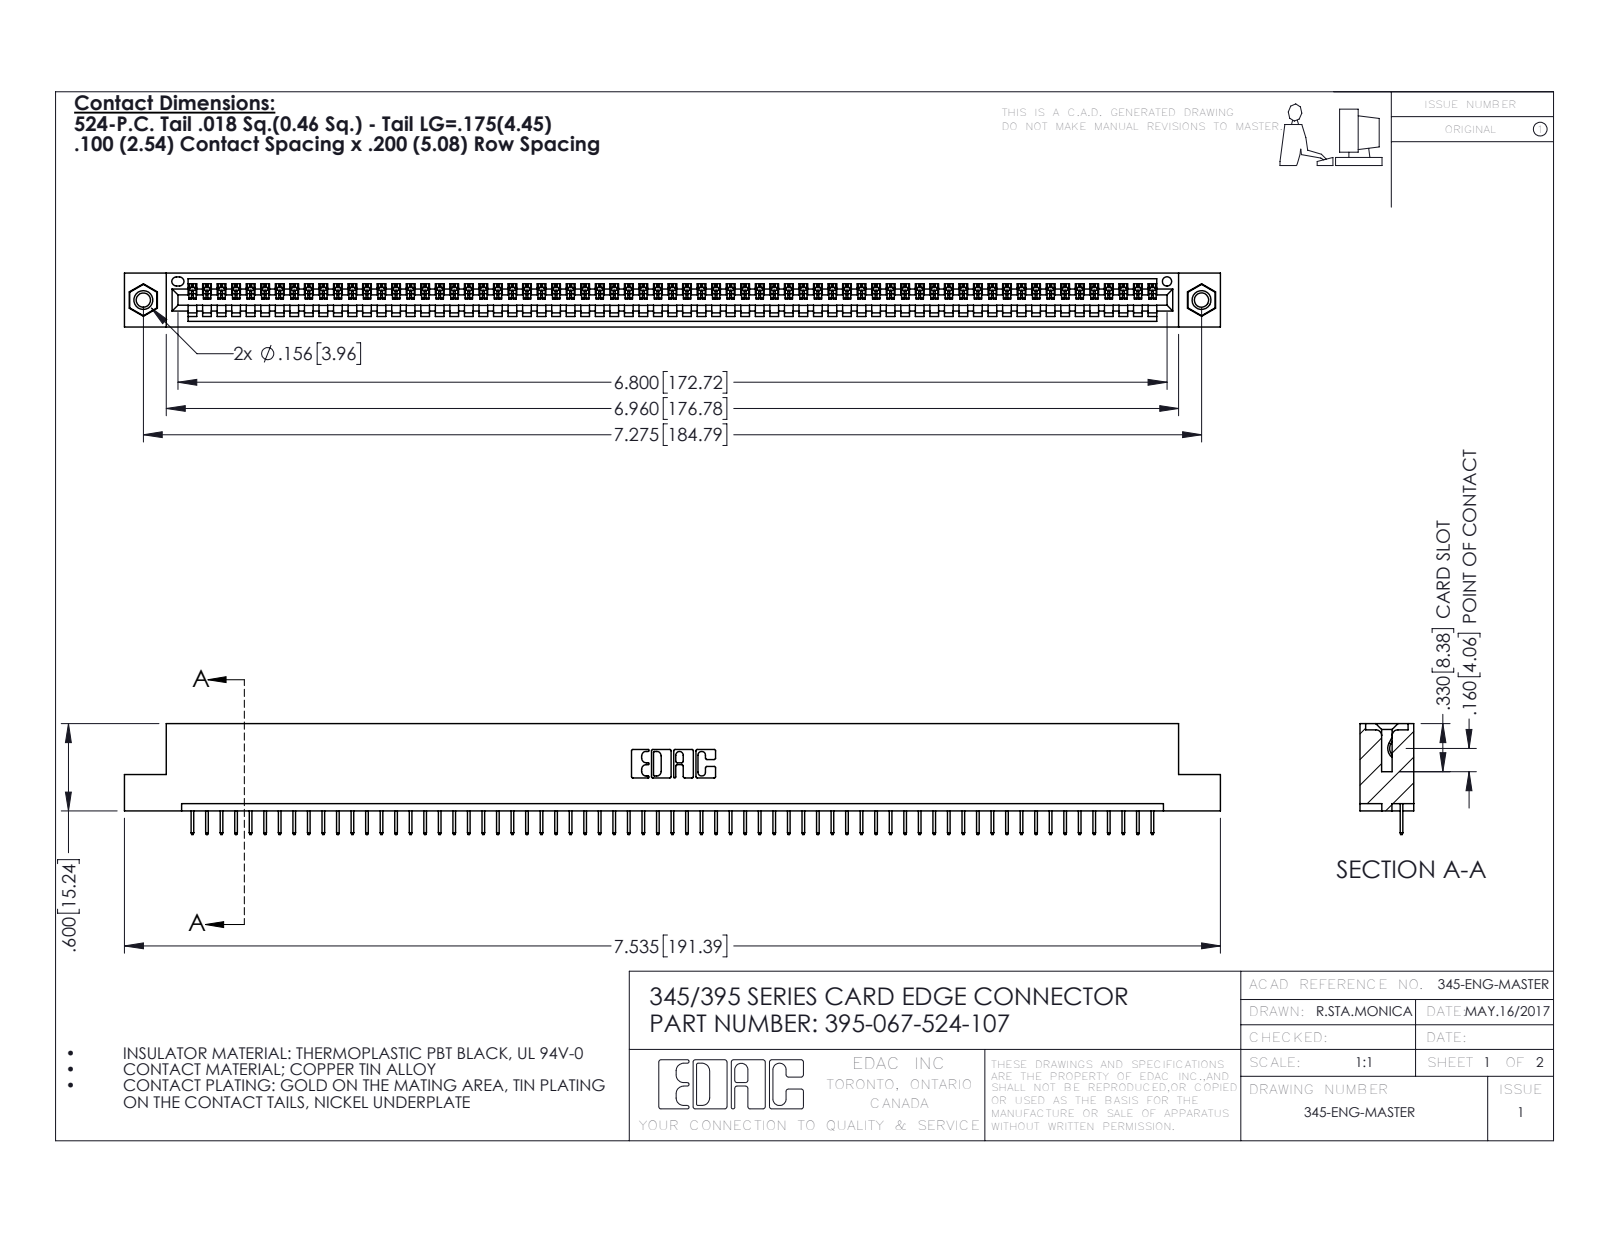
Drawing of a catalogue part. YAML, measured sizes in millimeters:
part_name: "345-292-001_345-293-124; 345 Part_Flush Mounting Lugs - 0.156 Dia-TI; 395-067-524-107; 345-250-001_345-250-005-103"
step_written_by: "SolidWorks 2016 (CONFIG_CONTROL_DESIGN)"
units: millimeters
bodies: {solids: 70, faces: 4340, planar: 3194, cylindrical: 1130, other: 16}
overall_size: [191.4, 19.4, 9.4]
volume: 18110
surface_area: 23590
round_holes:
  - {diameter: 2.5, count: 2}
  - {diameter: 3.2, count: 2}
  - {diameter: 4, count: 2}
  - {diameter: 1.6, count: 1}
round_bosses_or_shafts:
  - {diameter: 3.9, count: 2}
partial_cylinders:
  - {radius: 0.2, count: 134}
  - {radius: 0.3, count: 22}
  - {radius: 0.2, count: 6}
  - {radius: 0.8, count: 6}
  - {radius: 0.7, count: 3}
  - {radius: 0.8, count: 2}
  - {radius: 1, count: 2}
  - {radius: 0.4, count: 1}
face_to_face_distances: [1.8, 7.6, 9.4, 5.1, 2.5, 6.9, 0.6, 5.7, 1.8, 3.8]
hole_center_spacings: [6.9, 178.8, 184.8]
